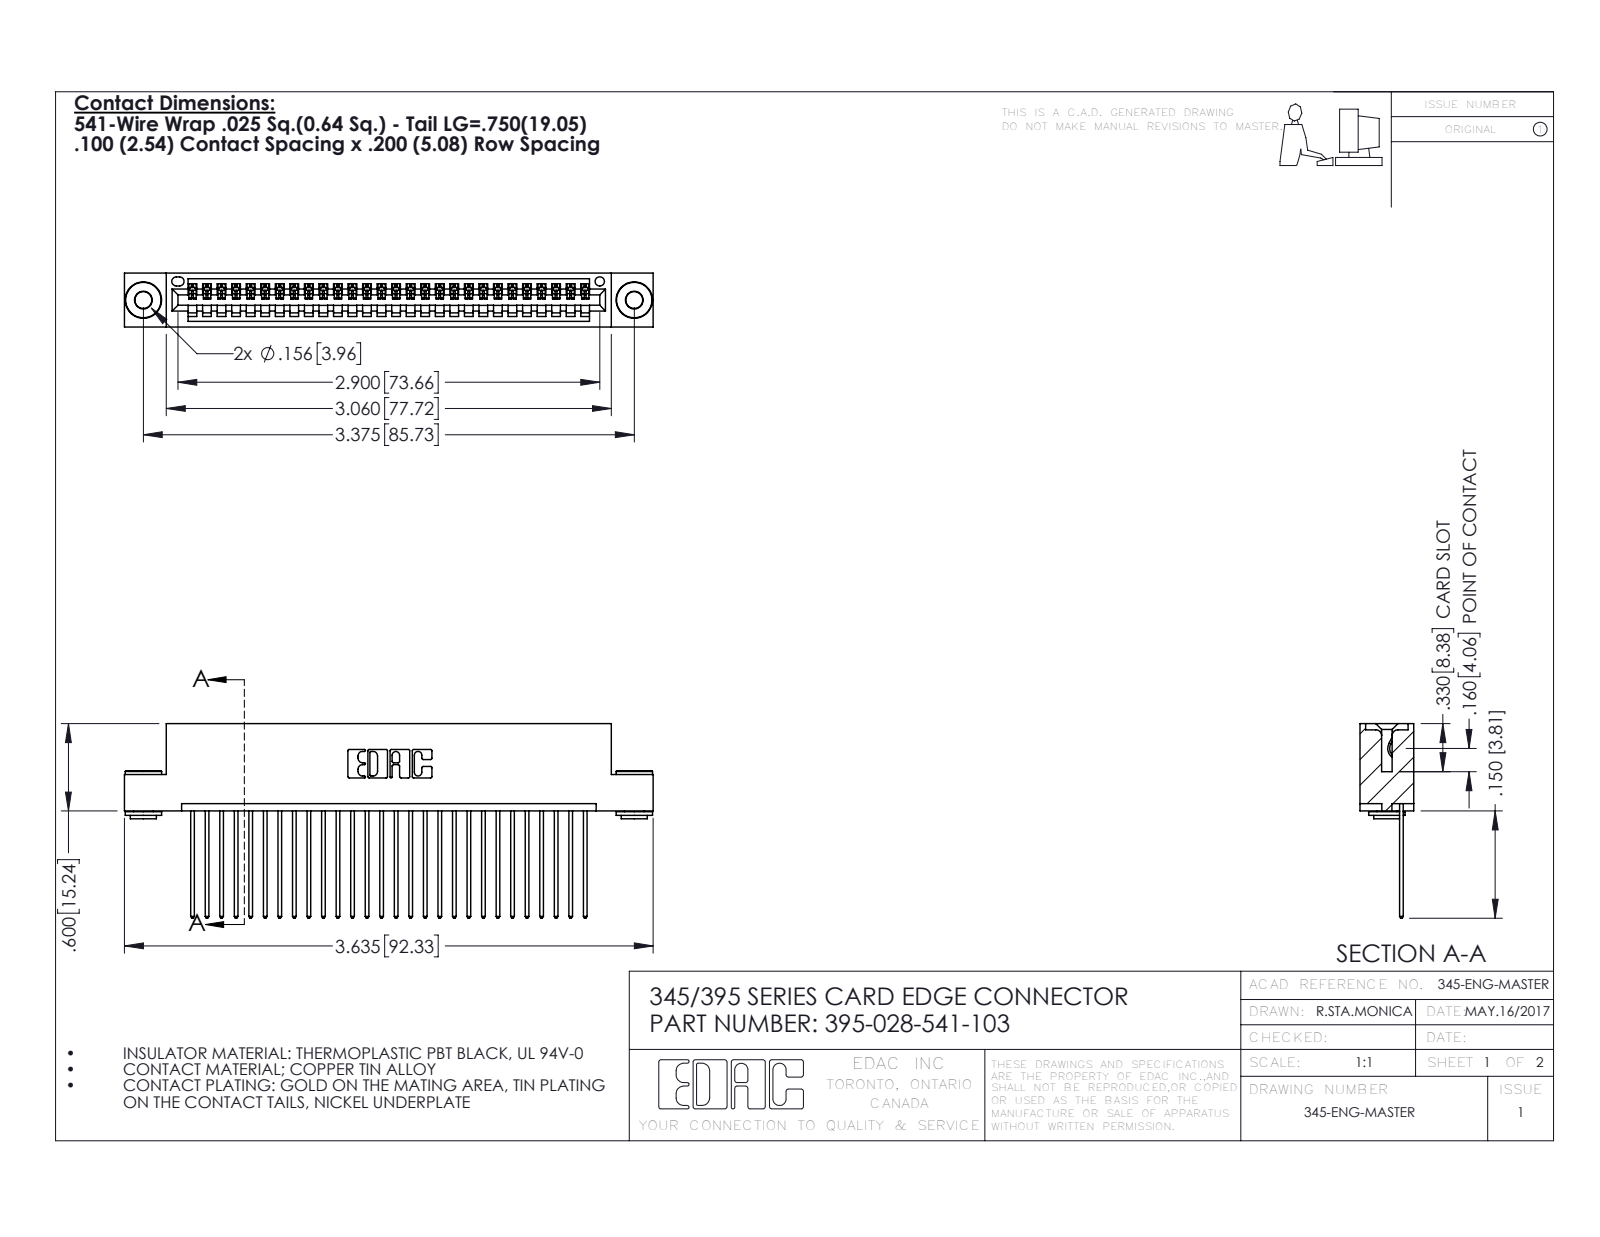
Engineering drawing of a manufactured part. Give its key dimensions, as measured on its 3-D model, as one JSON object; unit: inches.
{"part_name": "395-028-541-103; 345-292-001_345-293-141; 345 Part_Flush Mounting Lugs - 0.156 Dia-TH; 345-250-002_345-250-002-102", "step_written_by": "SolidWorks 2016 (CONFIG_CONTROL_DESIGN)", "units": "inches", "bodies": {"solids": 31, "faces": 1788, "planar": 1210, "cylindrical": 570, "other": 8}, "overall_size": [3.635, 1.337, 0.37], "volume_in3": 0.535, "surface_area_in2": 18.94, "round_holes": [[0.116, 2], [0.156, 2], [0.064, 1]], "round_bosses_or_shafts": [[0.25, 2], [0.18, 2], [0.136, 2]], "partial_cylinders_radius": [[0.006, 56], [0.01, 56], [0.01, 22], [0.007, 6], [0.031, 6], [0.026, 3], [0.031, 2], [0.04, 2]], "face_to_face_distances": [0.072, 0.298, 0.2, 0.025, 0.37, 0.098, 0.272, 0.225, 0.149, 0.072], "hole_center_spacings": [0.27, 3.14, 3.375]}
